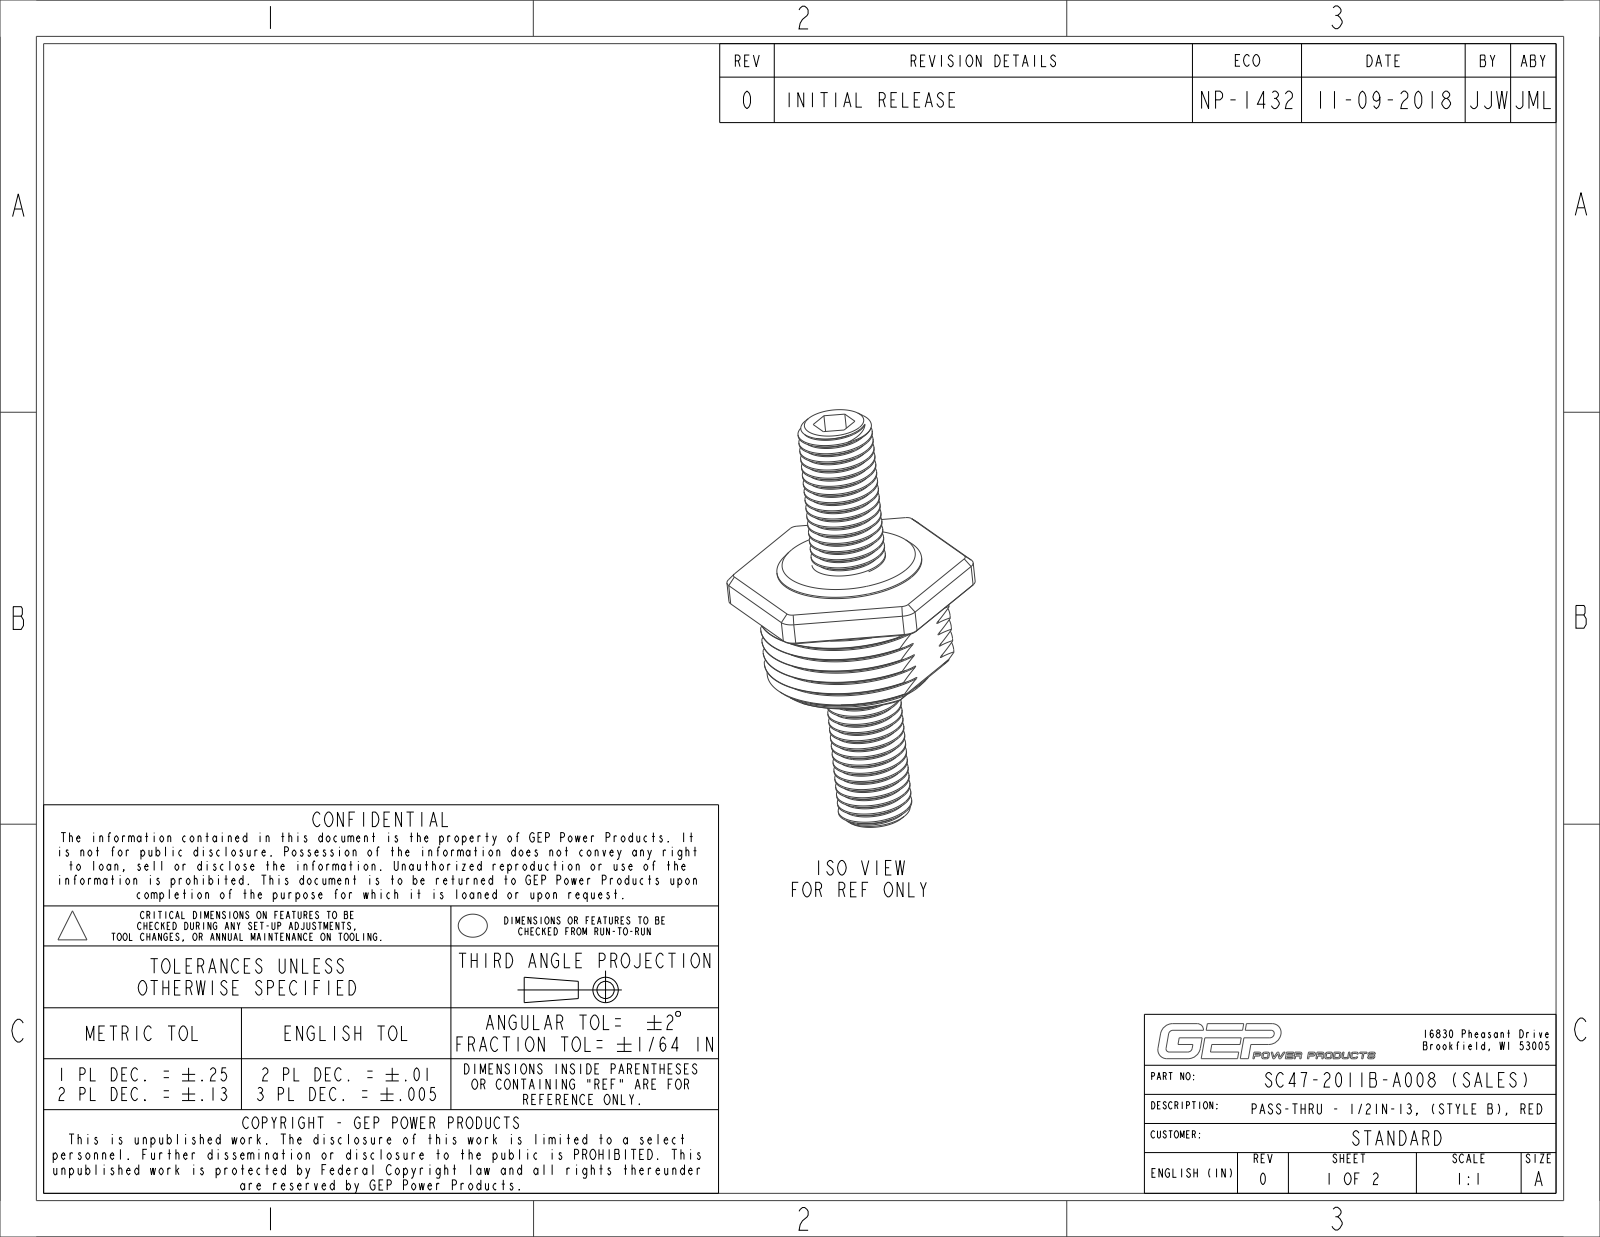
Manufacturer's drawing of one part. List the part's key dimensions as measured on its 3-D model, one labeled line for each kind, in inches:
Part name (STEP PRODUCT): SC47-2011B-A008_NCF_SW0001
STEP written by: CREO PARAMETRIC BY PTC INC, 2017110 (CONFIG_CONTROL_DESIGN)
Units: inches
Bodies: 1 solid, 289 faces (43 planar, 106 cylindrical, 140 other)
Overall size (bounding box): 3 × 1.701 × 1.5
Volume: 1.48 in³ · Surface area: 15.28 in²
Round holes (diameter × count): ⌀0.422 ×1
Round bosses / shafts (diameter × count): ⌀1 ×1, ⌀0.51 ×1
Partial cylindrical surfaces — rounded edges, fillets, slot ends (radius × count): R0.1 ×6, R0.181 ×6, R0.03 ×2, R0.652 ×1
Main face-to-face distances: 0.05, 0.85, 0.25, 0.2, 0.65, 0.9, 0.875, 0.625, 0.6, 1.5
